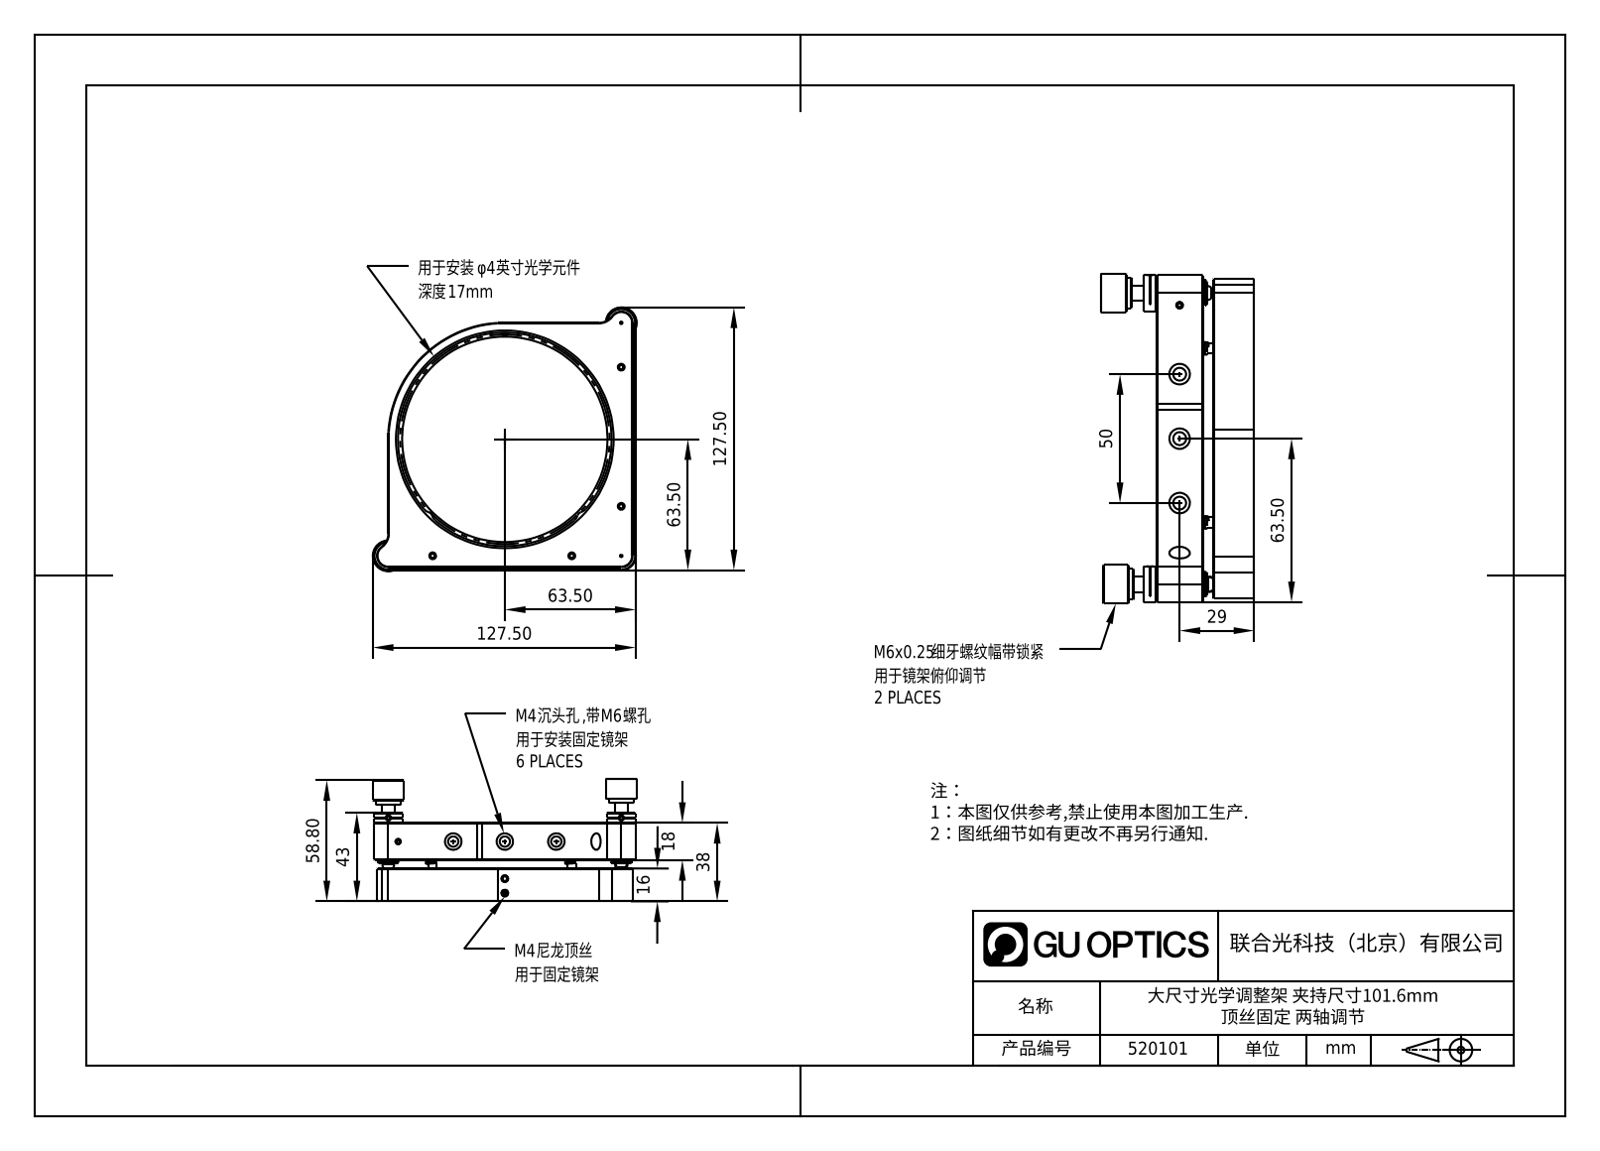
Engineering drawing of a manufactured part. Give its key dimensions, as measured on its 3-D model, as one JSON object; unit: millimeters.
{"part_name": "520101", "step_written_by": "SolidWorks 2020 (AUTOMOTIVE_DESIGN)", "units": "millimeters", "bodies": {"solids": 0, "faces": 314, "planar": 149, "cylindrical": 90, "other": 75}, "overall_size": [128, 128, 59.78], "round_holes": [[5, 6], [8, 6], [6.5, 4], [9.5, 3], [2.5, 2], [1.2, 1], [10, 1]], "round_bosses_or_shafts": [[3.3, 6], [4, 4], [2, 4], [3, 3], [15, 2], [14, 2], [6, 2], [103.6, 1]], "partial_cylinders_radius": [[5, 10], [1.05, 8], [5.5, 3], [0.2, 2], [2.5, 2], [8, 2], [10, 2], [7, 1]], "face_to_face_distances": [16, 22, 38, 4, 18, 20, 1.5, 1, 118.5, 120], "hole_center_spacings": [25, 21.5, 24, 26.75, 50, 51.75, 67.5, 76.75]}
